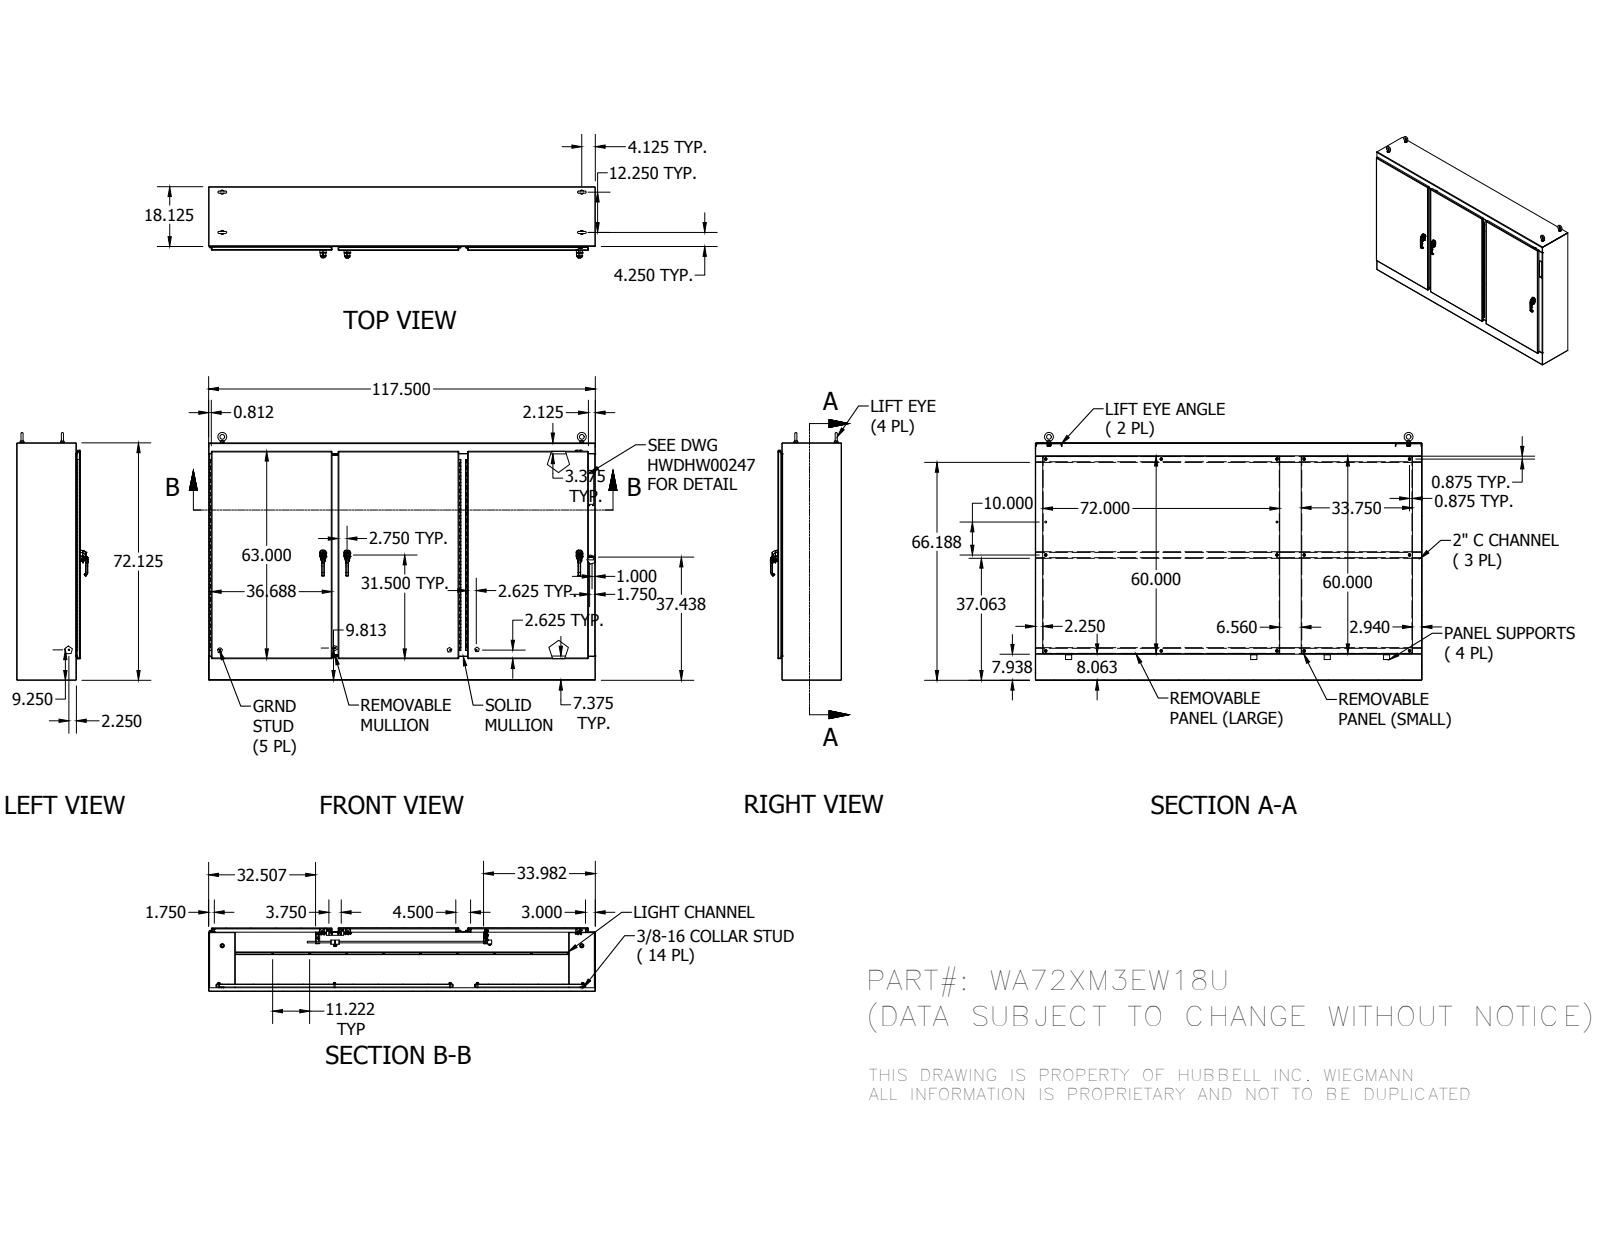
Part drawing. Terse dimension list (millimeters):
name: WAXM3EW18U_TOP; HFW3025; 316298; 349132 (+8 more)
written by: Autodesk Inventor 2014 (AUTOMOTIVE_DESIGN)
unit: mm
bodies: 334 solids, 12539 faces (5742 planar, 4036 cylindrical, 2761 other)
size: 2984.5 × 1911.29 × 548.73
volume: 73 280 000 mm³; area: 46 080 000 mm²
holes: 28× ⌀6.35, 26× ⌀9.52, 20× ⌀7.02, 16× ⌀14.29, 14× ⌀7.8, 12× ⌀5.08, 10× ⌀4.83, 10× ⌀7.14, 10× ⌀7.33, 10× ⌀8.51, 10× ⌀9.65, 9× ⌀5.4
bosses: 27× ⌀8.38, 25× ⌀6.35, 21× ⌀15.88, 17× ⌀9.52, 15× ⌀8.56, 13× ⌀14.29, 10× ⌀25.4, 10× ⌀12.7
rounds: 525× R0.5, 323× R0.3, 240× R0.51, 63× R0.47, 52× R1.27, 47× R1.59, 41× R2, 33× R1
face distances: 3.17, 488.43, 3.18, 50.8, 1.59, 53.97, 57.15, 53.98, 485.26, 434.46
hole spacings: 1.6, 285.04, 1390.33, 1.59, 570.08, 1380.8, 739.77, 855.12
